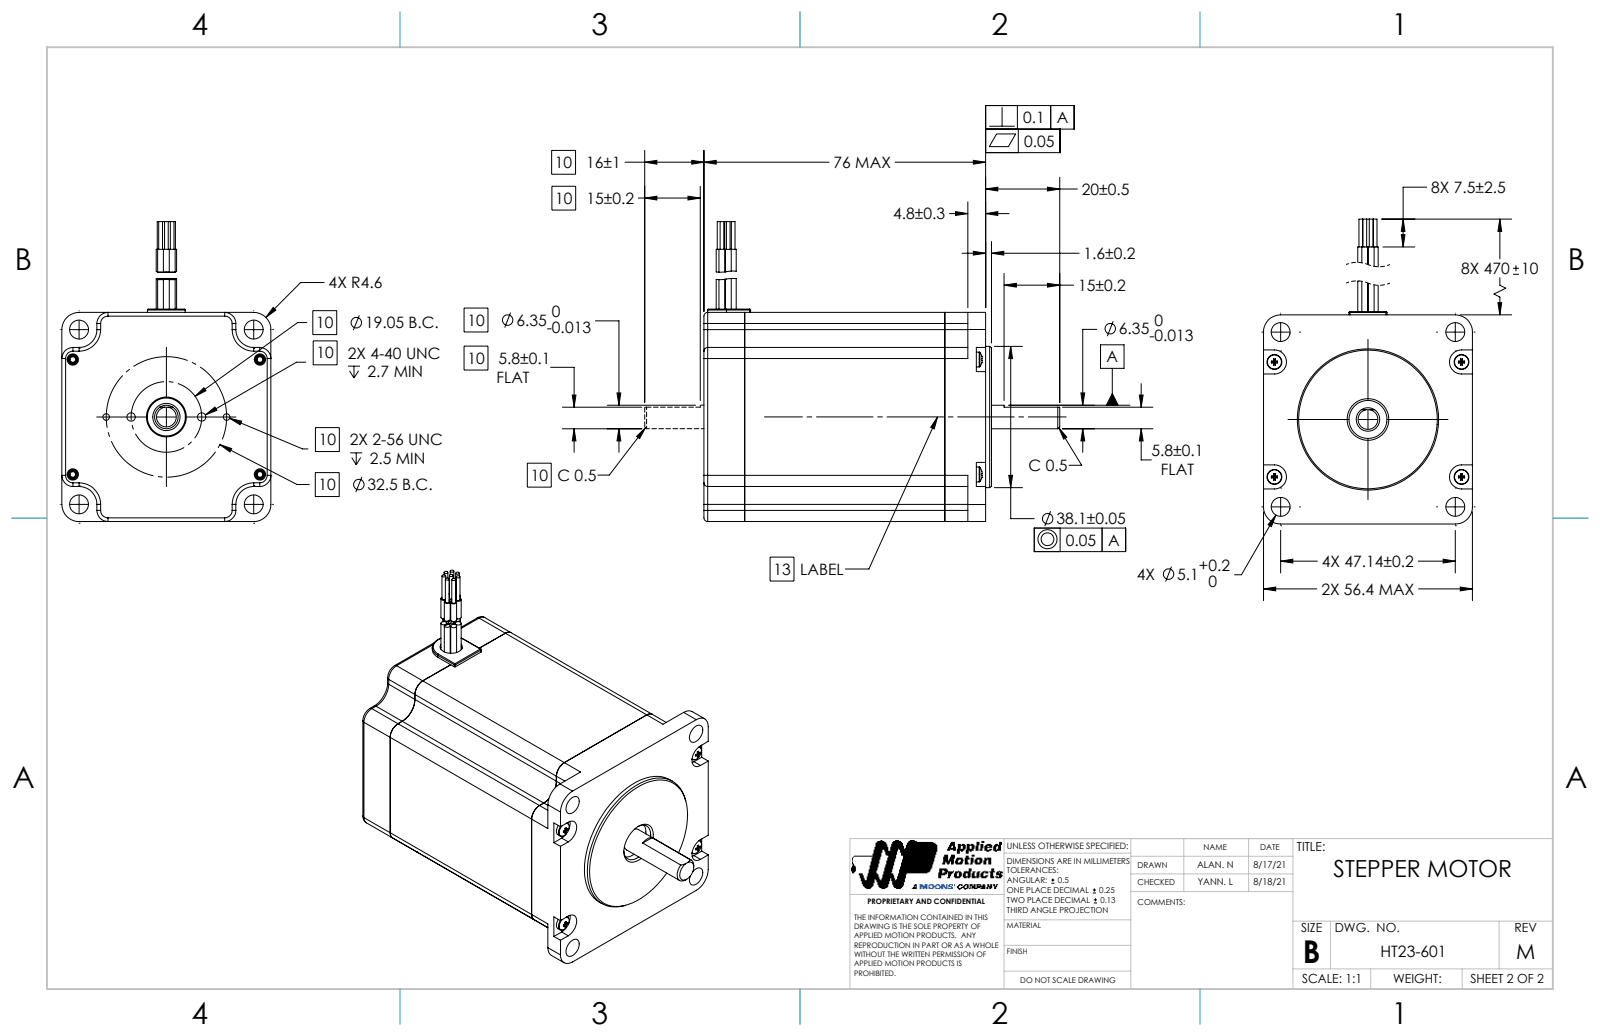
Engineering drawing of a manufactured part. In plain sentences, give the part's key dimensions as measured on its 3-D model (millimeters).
The part is named "HT23-601_RevM; HT23 REAR ENDBELL ASSEMBLY; HT23-601 Laminations; HT23 Wire Grommet (+6 more)". Its 3-D file was written by "SolidWorks 2017 (AUTOMOTIVE_DESIGN)". It is 32 solids with 420 faces: 162 planar, 198 cylindrical and 60 other. Overall it measures 96 by 80.9 by 56.4 millimeters. Its volume is 217 062 cubic millimeters and its surface area 41 402 square millimeters. Round holes: 4 of diameter 2.5, 4 of diameter 3.4, 4 of diameter 5.1, 1 of diameter 6, 1 of diameter 6.35, 1 of diameter 10.25. Round bosses or shafts: 8 of diameter 1.6, 8 of diameter 1, 4 of diameter 4, 4 of diameter 2, 1 of diameter 38.1. Partial cylindrical surfaces (rounded edges, fillets, slot ends): 8 of radius 1, 8 of radius 3, 5 of radius 0.25, 4 of radius 3.25, 4 of radius 4.6, 4 of radius 4.82, 4 of radius 10, 1 of radius 5.1. The main face-to-face distances are 54, 56.4, 65, 11, 76, 12.6, 1.6, 77.6, 66.6, 9.45. The hole center spacings are 8.24, 29.63, 33.33, 39.11, 47.14, 49.48, 62.53, 31.
